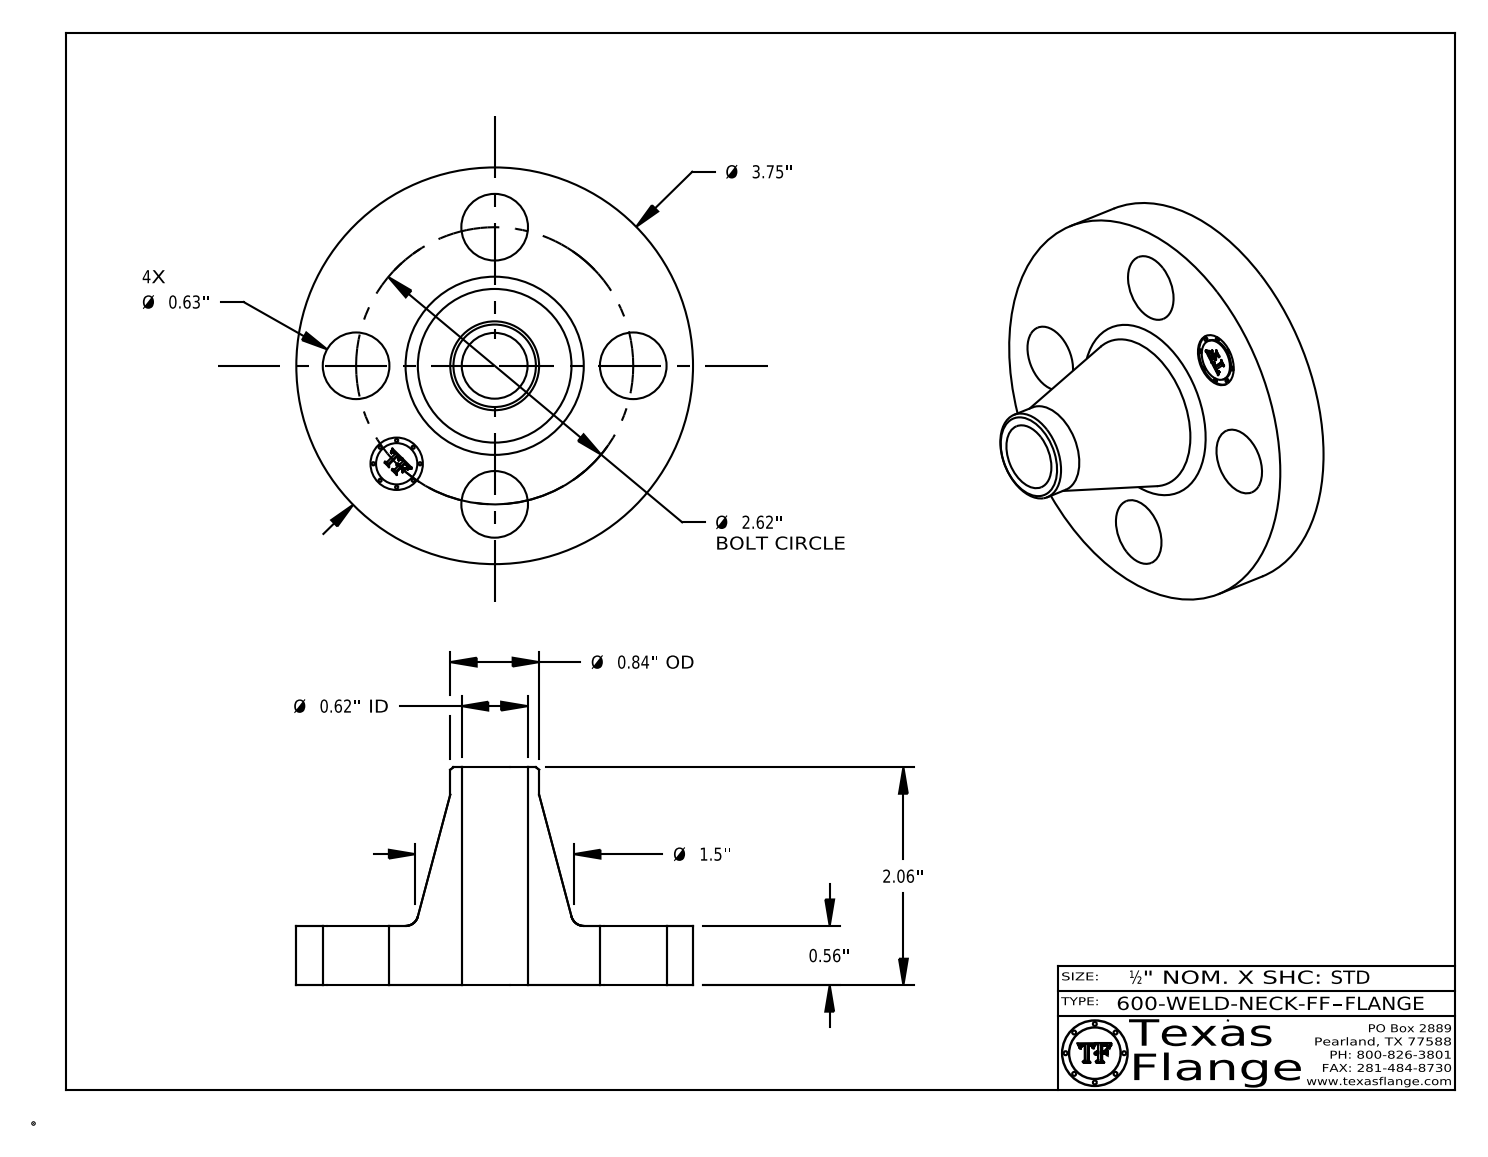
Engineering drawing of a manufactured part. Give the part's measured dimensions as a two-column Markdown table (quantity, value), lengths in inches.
| quantity | value |
| --- | --- |
| part name | 600-WELD-NECK-FF |
| STEP written by | CATIA V5 STEP AP214 (AUTOMOTIVE_DESIGN) |
| units | inches |
| bodies | 1 solid, 408 faces (368 planar, 34 cylindrical, 6 other) |
| overall size | 3.75 × 3.75 × 2.06 |
| volume | 6.379 in³ |
| surface area | 38.16 in² |
| round holes (diameter × count) | 0.63 × 4, 0.495 × 1, 0.622 × 1 |
| round bosses / shafts (diameter × count) | 0.03 × 8, 3.75 × 1, 0.84 × 1, 0.39 × 1 |
| main face-to-face distances | 0.56, 2.06, 1.5, 0.545, 0.015, 1.515, 0.148, 0.144, 0.027, 0.096 |
| hole center spacings | 1.31, 1.852, 1.003, 2.42, 2.62, 1.31 |
